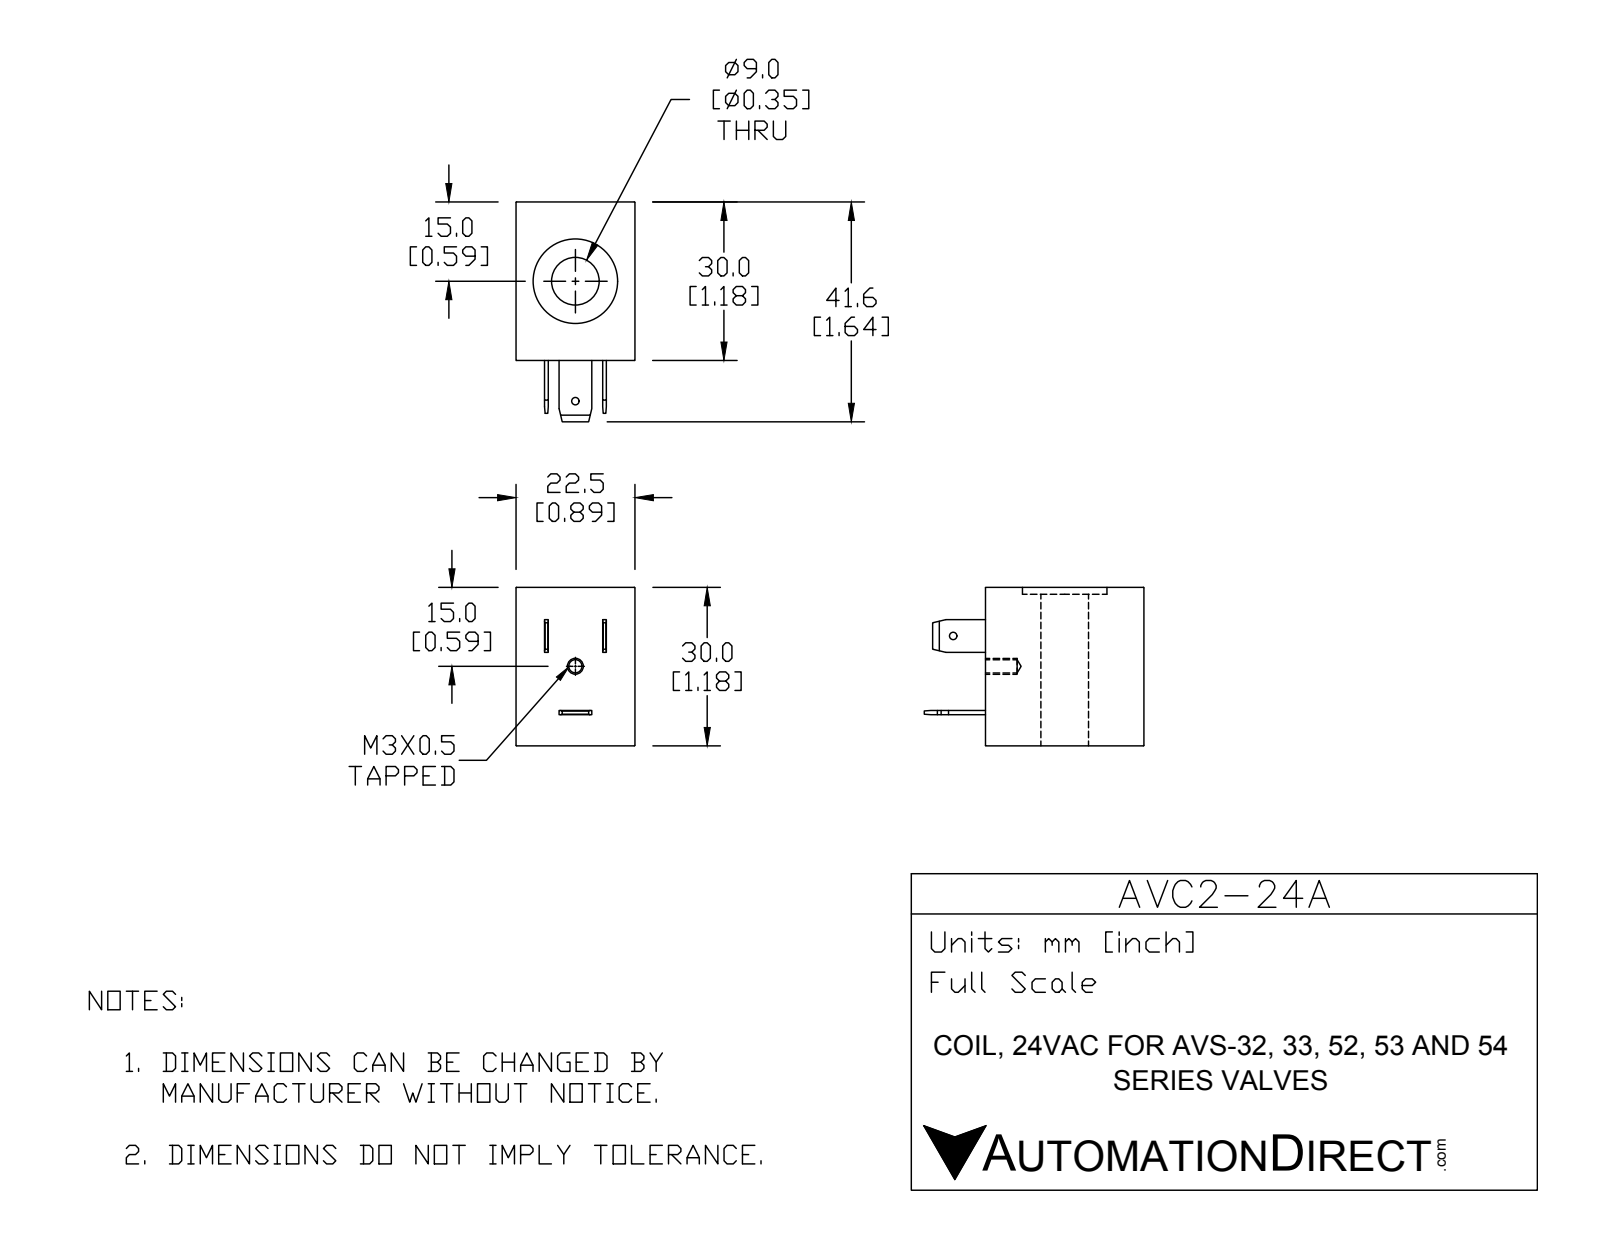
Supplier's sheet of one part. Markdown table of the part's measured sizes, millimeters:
| quantity | value |
| --- | --- |
| part name | AVC2-24A |
| STEP written by | SolidWorks 2016 (AUTOMOTIVE_DESIGN) |
| units | millimeters |
| bodies | 1 solid, 60 faces (34 planar, 20 cylindrical, 6 other) |
| overall size | 41.6 × 30 × 22.5 |
| volume | 18 267 mm³ |
| surface area | 5 712 mm² |
| round holes (diameter × count) | 1.4 × 2, 2.5 × 1, 9 × 1, 16 × 1 |
| partial cylindrical surfaces (radius × count) | 0.1 × 8 |
| main face-to-face distances | 30, 22.5, 28.7, 1.3, 11, 6.1, 16.4, 5.4, 17.1, 0.7 |
| hole center spacings | 22.7 |
